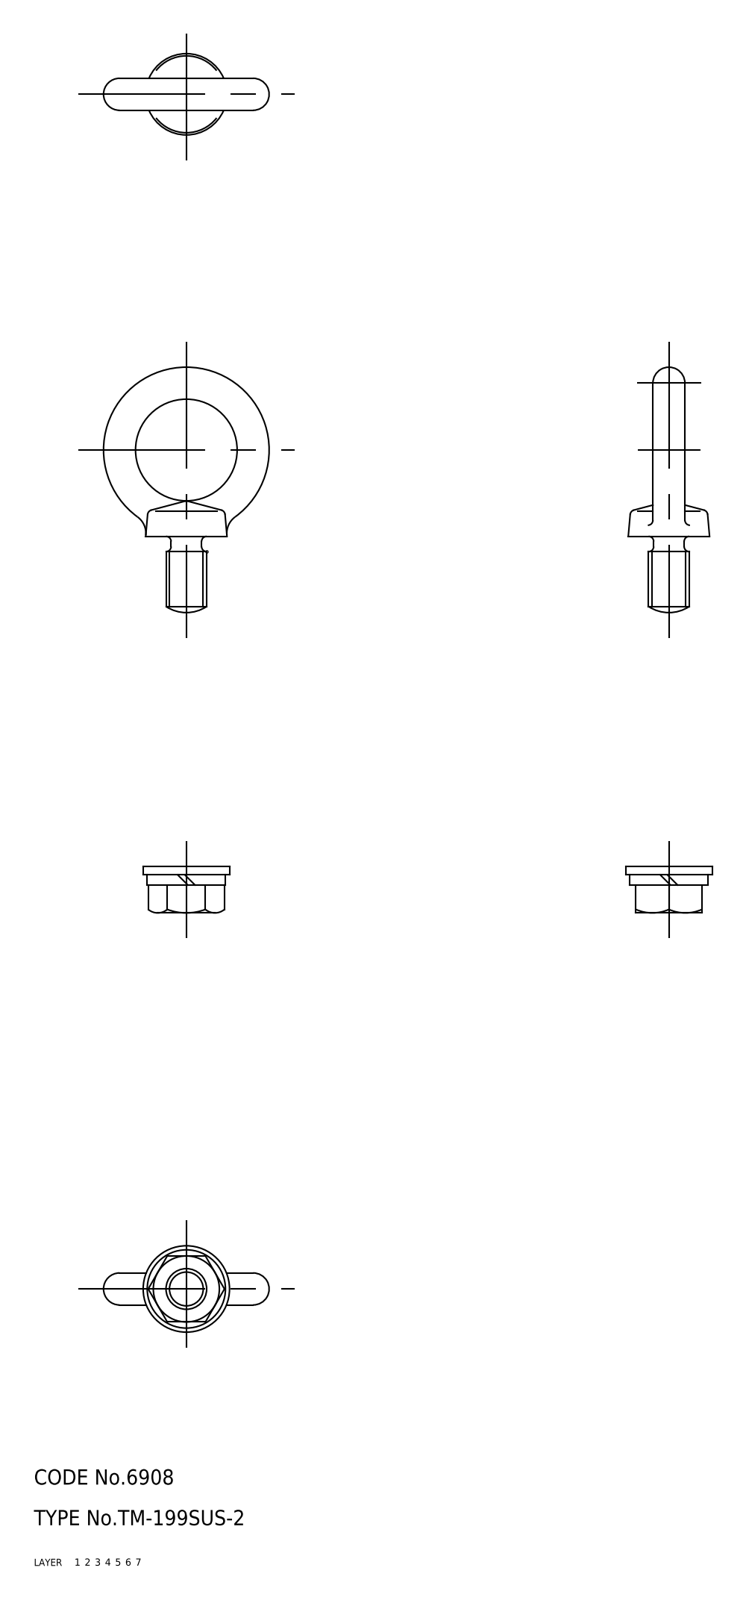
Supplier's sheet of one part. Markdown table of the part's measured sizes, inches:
| quantity | value |
| --- | --- |
| part name | TM_199SUS_2 |
| STEP written by | SolidWorks 2003240 (AUTOMOTIVE_DESIGN) |
| units | inches |
| bodies | 4 solids, 52 faces (13 planar, 12 cylindrical, 27 other) |
| overall size | 1.902 × 1.283 × 0.669 |
| volume | 0.312 in³ |
| surface area | 5.856 in² |
| round holes (diameter × count) | 0.315 × 1 |
| round bosses / shafts (diameter × count) | 0.669 × 1, 0.606 × 1 |
| main face-to-face distances | 0.063, 0.079, 0.142, 0.512, 0.217, 0.295, 0.358 |
